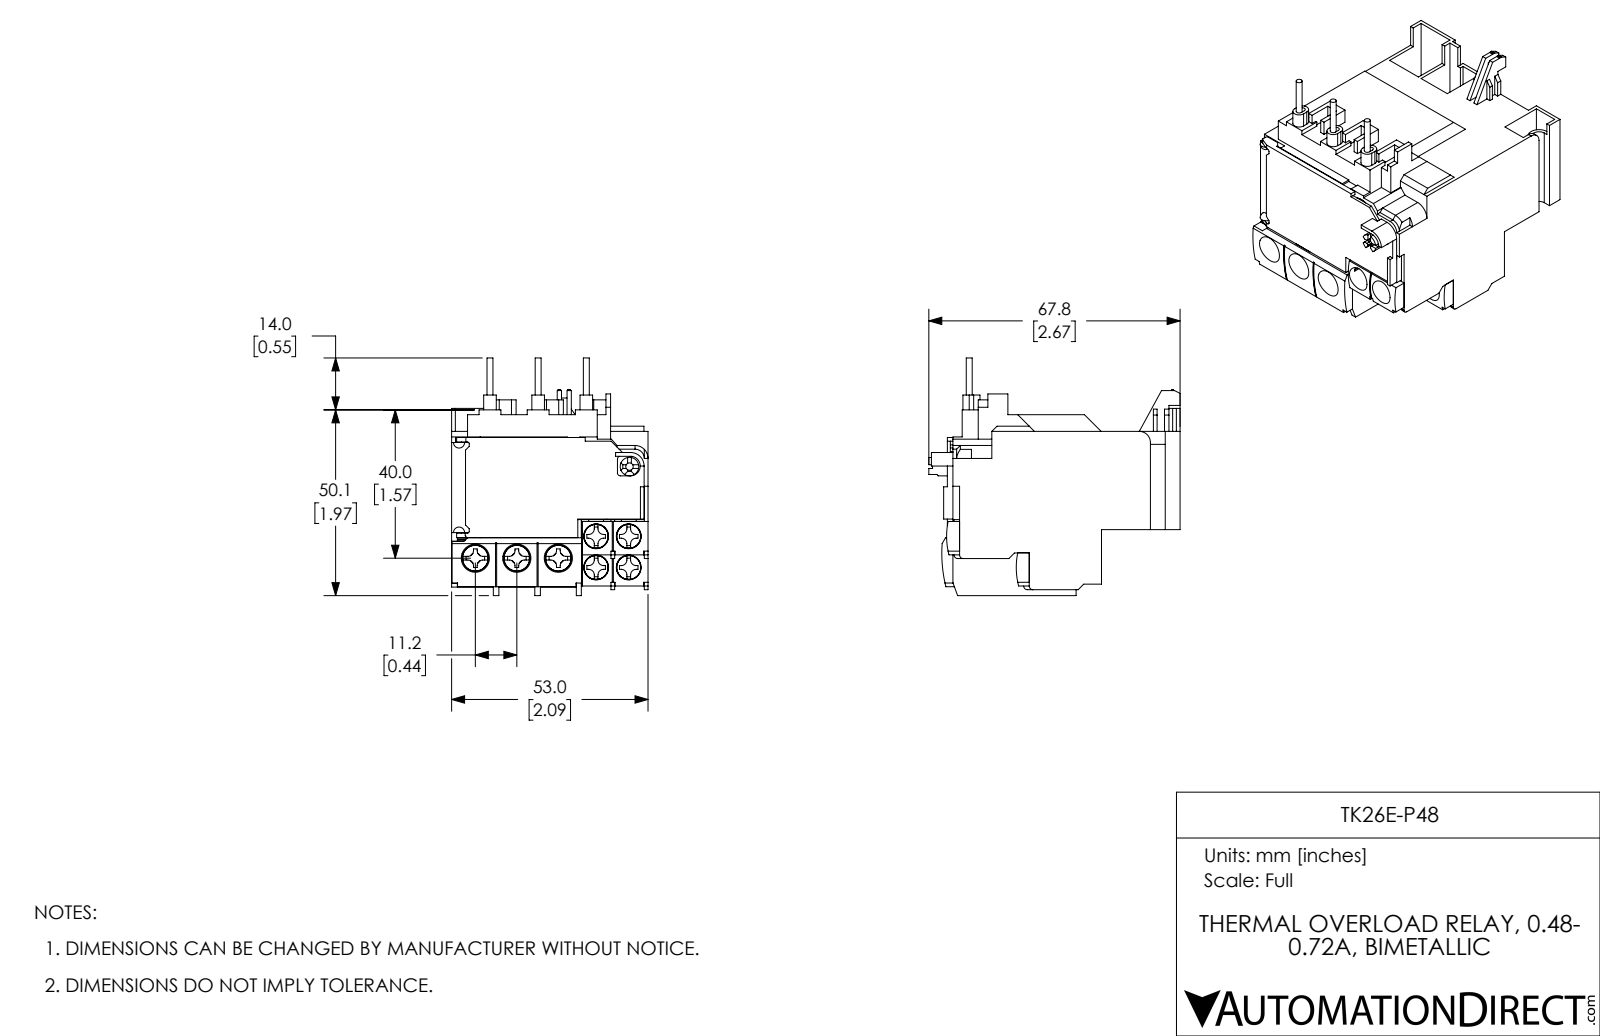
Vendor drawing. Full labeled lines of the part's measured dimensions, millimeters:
Part name (STEP PRODUCT): TK26E-P48
STEP written by: SolidWorks 2017 (AUTOMOTIVE_DESIGN)
Units: millimetres
Bodies: 38 solids, 1480 faces (1225 planar, 220 cylindrical, 35 other)
Overall size (bounding box): 67.8 × 64.1 × 53
Volume: 99 940 mm³ · Surface area: 38 810 mm²
Round holes (diameter × count): ⌀3.5 ×4, ⌀3.6 ×4, ⌀6.7 ×4, ⌀4 ×3, ⌀4.1 ×3, ⌀7.6 ×3, ⌀1 ×1, ⌀2 ×1, ⌀5 ×1, ⌀11 ×1
Round bosses / shafts (diameter × count): ⌀6.6 ×4, ⌀1.6 ×3, ⌀6 ×1
Partial cylindrical surfaces — rounded edges, fillets, slot ends (radius × count): R1.5 ×28, R1 ×8, R0.5 ×6, R1.7 ×6, R0.8 ×5, R1.2 ×4, R4.3 ×4, R4.8 ×3
Main face-to-face distances: 1, 9, 1.5, 12, 53, 2, 10, 11, 8.7, 0.7
Hole centre spacings: 8.4, 8.8, 11.2, 12.2, 9.6, 10.5, 11.8, 18.8
